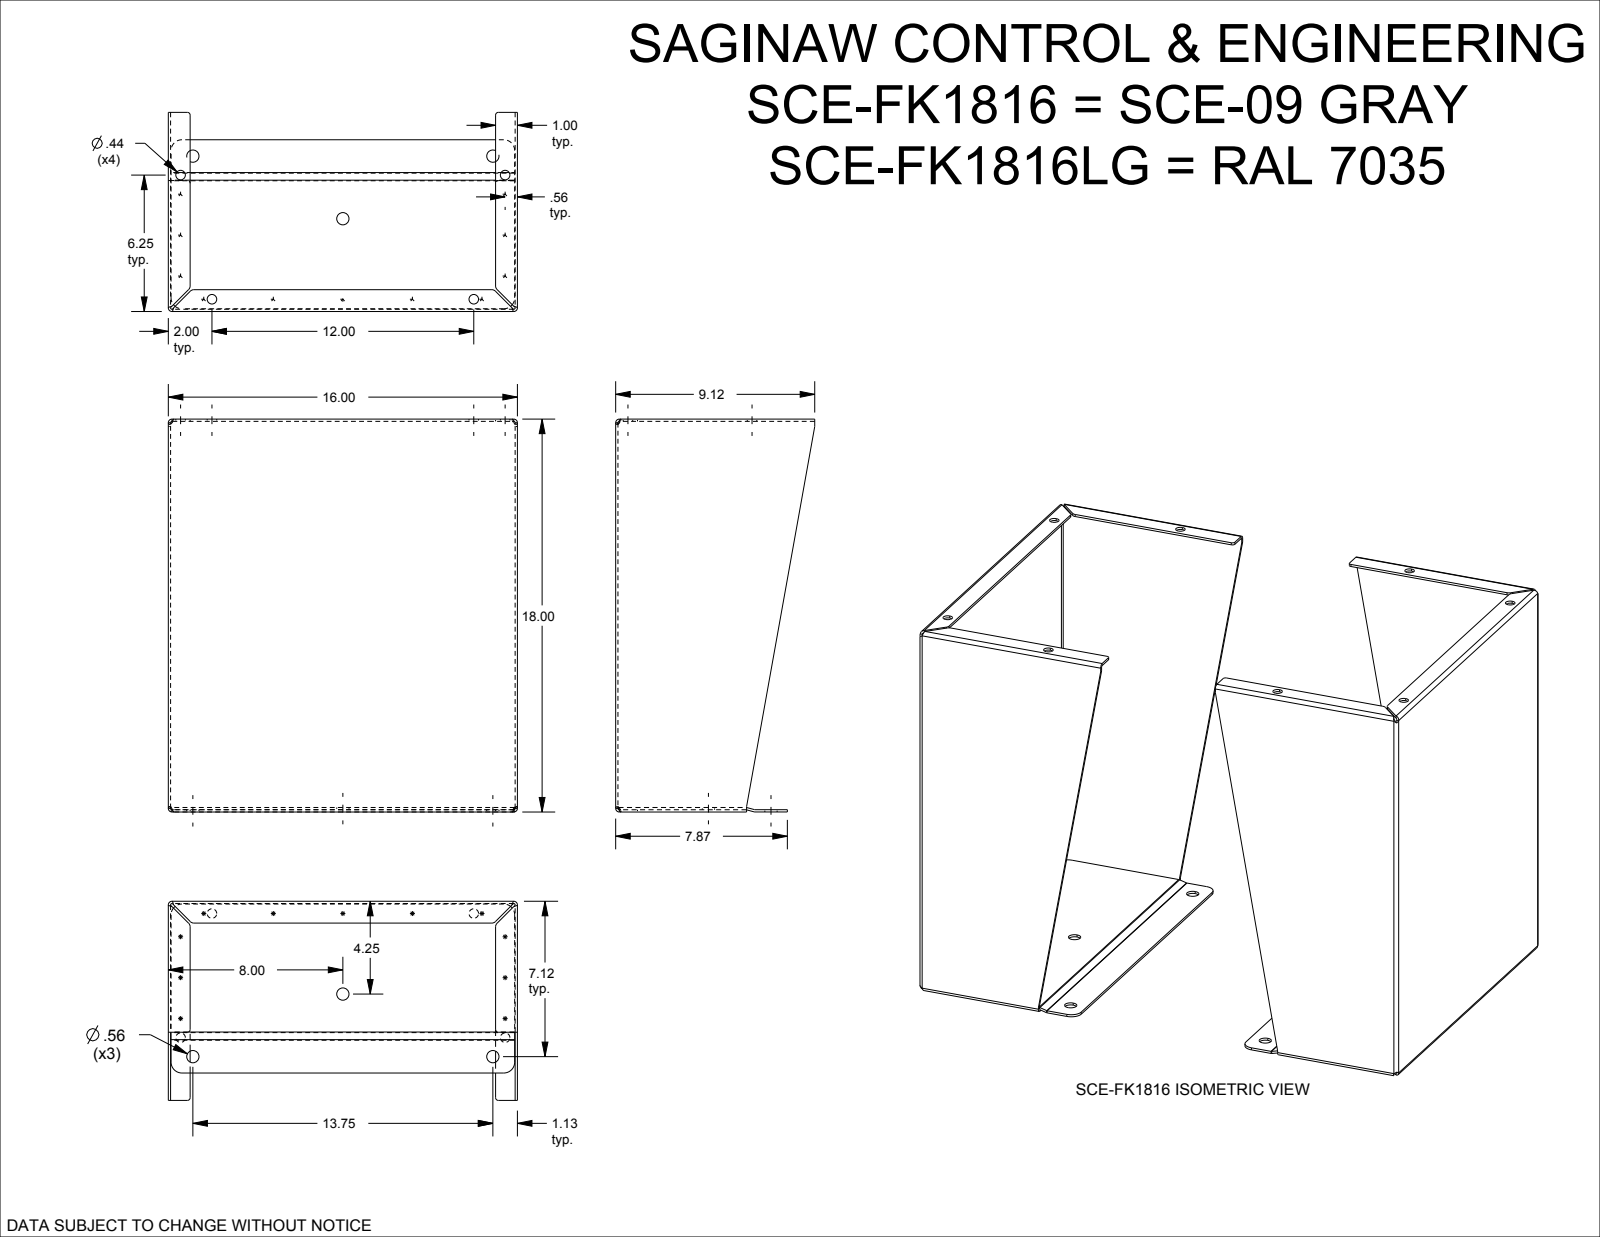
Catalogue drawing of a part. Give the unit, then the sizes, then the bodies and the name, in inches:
Units: inches
Overall size (bounding box): 24 × 18 × 16
Round holes (diameter × count): ⌀0.437 ×8, ⌀0.563 ×6
Partial cylindrical surfaces — rounded edges, fillets, slot ends (radius × count): R0.166 ×16, R0.062 ×12, R0.125 ×8, R0.22 ×8, R0.5 ×8, R0.063 ×4
Main face-to-face distances: 0.104, 23.896, 15.896, 23.792, 24, 16, 15.792, 17.792, 17.896, 0.101
Hole centre spacings: 1.035, 5.866, 6.614, 7.043, 7.449, 7.701, 10.646, 14.38
Volume: 150.5 in³ · Surface area: 2 928 in²
Bodies: 4 solids, 214 faces (96 planar, 86 cylindrical, 32 other)
Part name (STEP PRODUCT): SCE-FK1816
STEP written by: SolidWorks 2019 (CONFIG_CONTROL_DESIGN)
